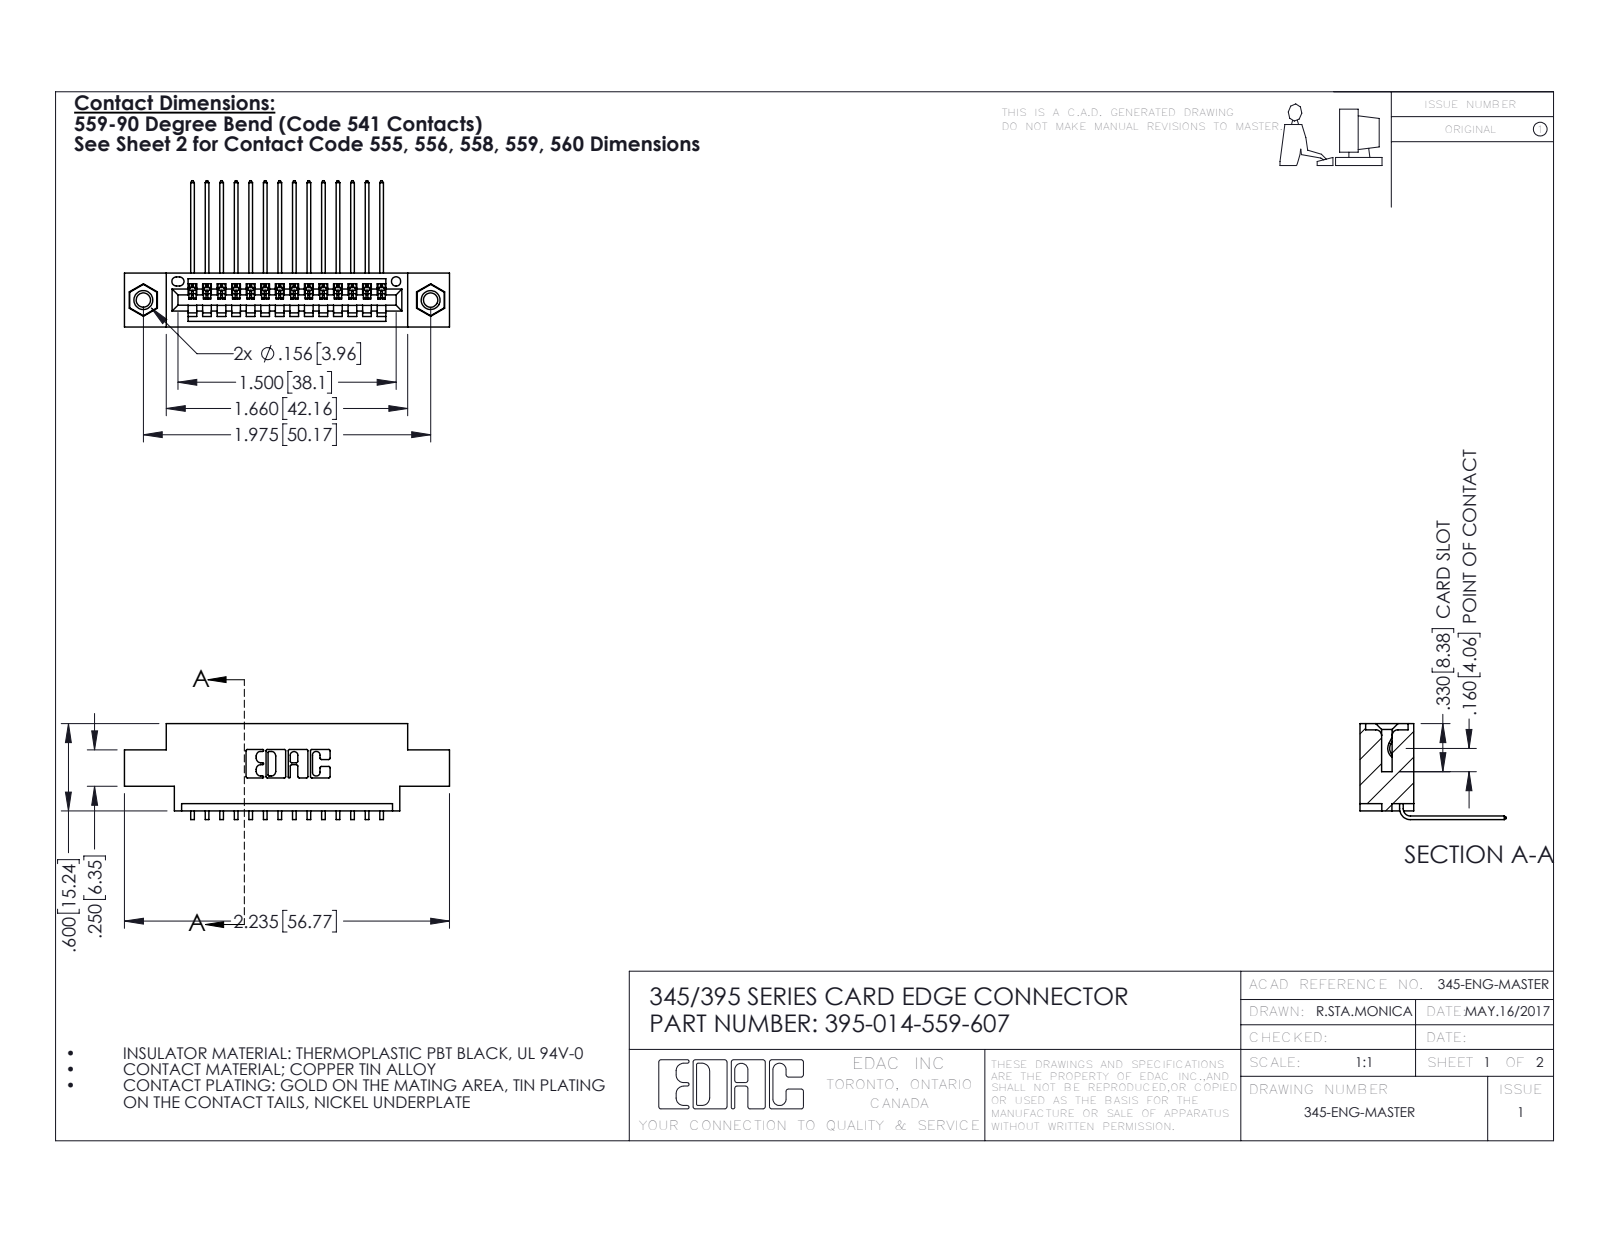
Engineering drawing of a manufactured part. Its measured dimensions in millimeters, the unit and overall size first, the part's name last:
Units: millimetres
Overall size (bounding box): 56.8 × 25.5 × 16.7
Round holes (diameter × count): ⌀2.5 ×2, ⌀3.2 ×2, ⌀4 ×2, ⌀1.6 ×1
Round bosses / shafts (diameter × count): ⌀3.9 ×2
Partial cylindrical surfaces — rounded edges, fillets, slot ends (radius × count): R0.2 ×28, R0.3 ×22, R0.2 ×6, R0.8 ×6, R0.7 ×3, R0.8 ×2, R1 ×2, R0.4 ×1
Main face-to-face distances: 9.4, 1.8, 7.6, 5.1, 2.5, 6.9, 0.6, 2.5, 5.7, 3.8
Hole centre spacings: 6.9, 44.2, 50.2
Volume: 5 080 mm³ · Surface area: 6 806 mm²
Bodies: 17 solids, 1030 faces (704 planar, 310 cylindrical, 16 other)
Part name (STEP PRODUCT): 395-014-559-607; 345-292-001_558 559 Tail - 1; 345 Part_0.170 Offset - 0.156 Dia-TI; 345-250-001_345-250-005-103
STEP written by: SolidWorks 2016 (CONFIG_CONTROL_DESIGN)
